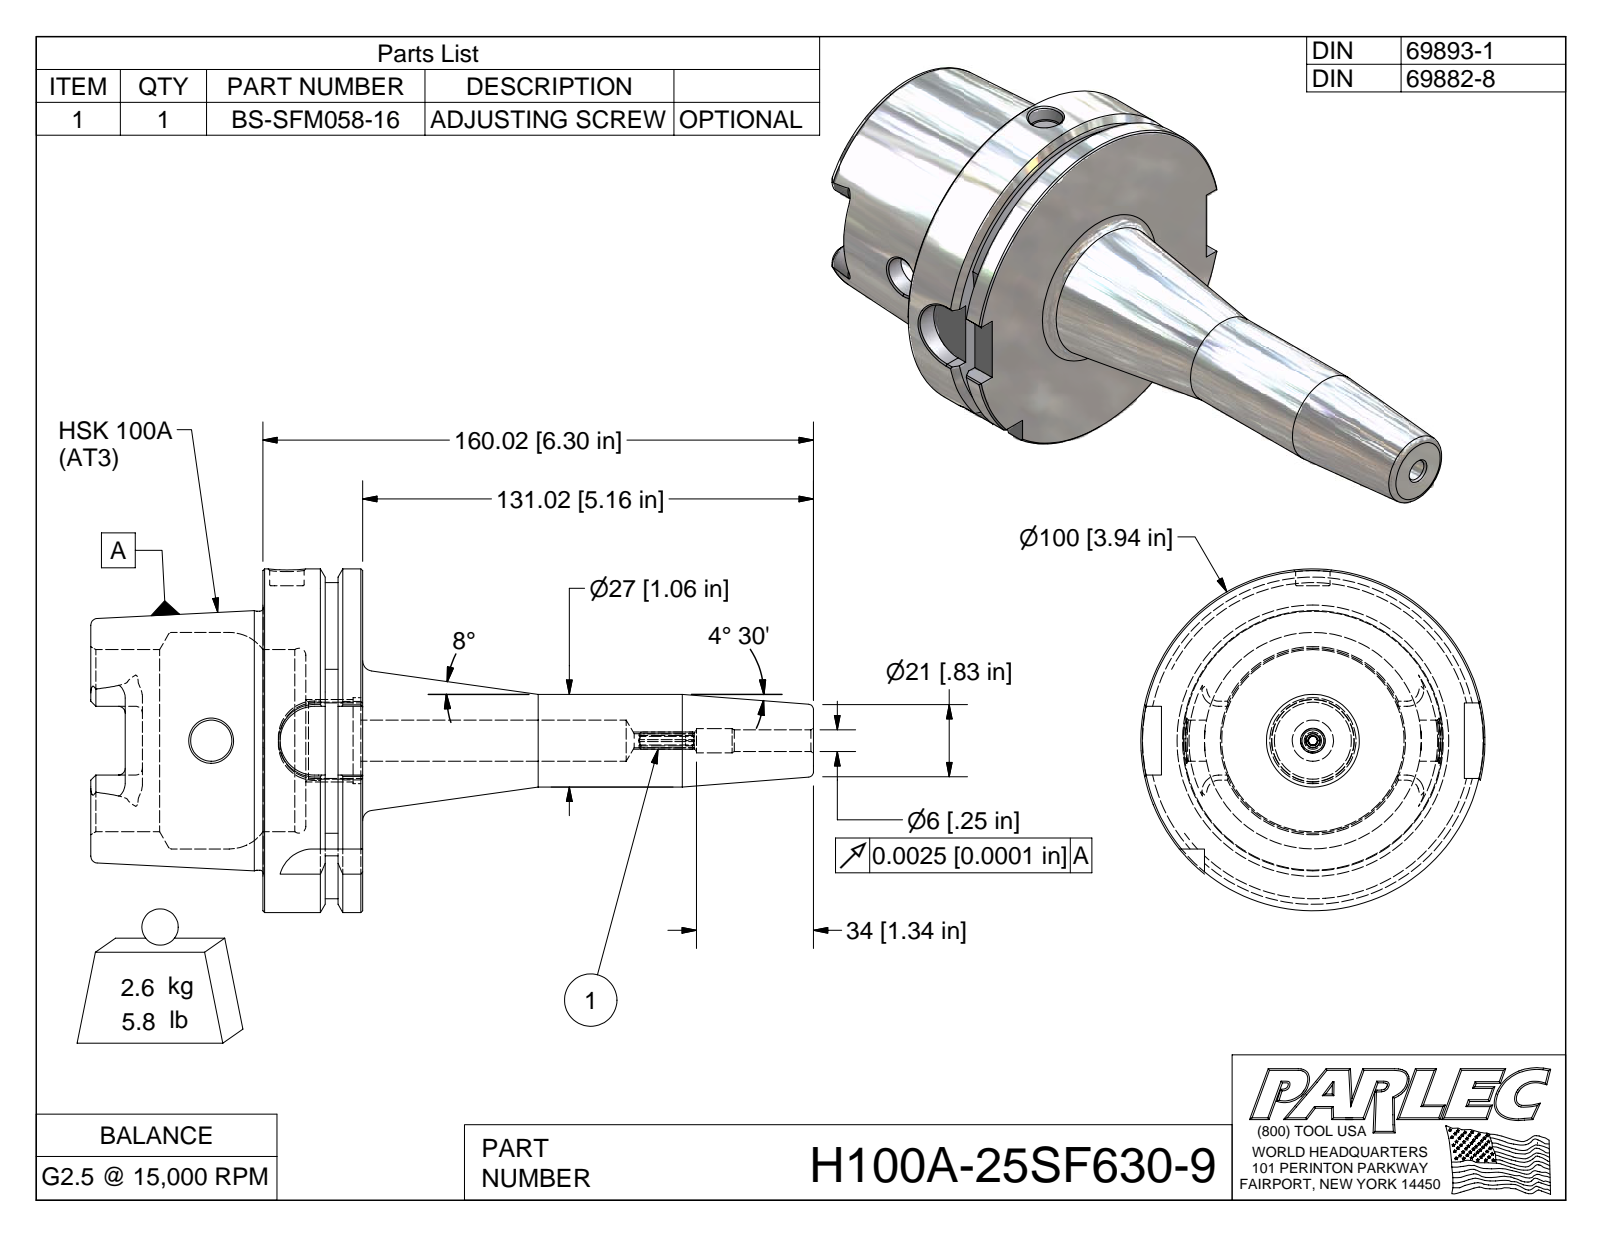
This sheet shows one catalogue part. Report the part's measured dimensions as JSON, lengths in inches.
{"part_name": "H100A-25SF630-9; H100A-25SF630-9-1; BS-SFM058-16", "step_written_by": "Autodesk Inventor 2009 (AUTOMOTIVE_DESIGN)", "units": "inches", "bodies": {"solids": 2, "faces": 150, "planar": 49, "cylindrical": 30, "other": 71}, "overall_size": [8.269, 3.937, 3.937], "volume_in3": 20.3, "surface_area_in2": 100.9, "round_holes": [[0.25, 1], [0.28, 1], [0.394, 1], [0.472, 1], [0.881, 1], [0.985, 1], [2.087, 1], [2.48, 1]], "round_bosses_or_shafts": [[3.937, 1], [2.967, 1], [1.063, 1]], "partial_cylinders_radius": [[0.394, 4], [0.079, 3], [0.192, 2], [0.098, 1], [1.811, 1]], "face_to_face_distances": [1.142, 0.492, 0.65, 1.969, 2.461, 3.11, 2.682, 0.713, 0.221, 0.428]}
